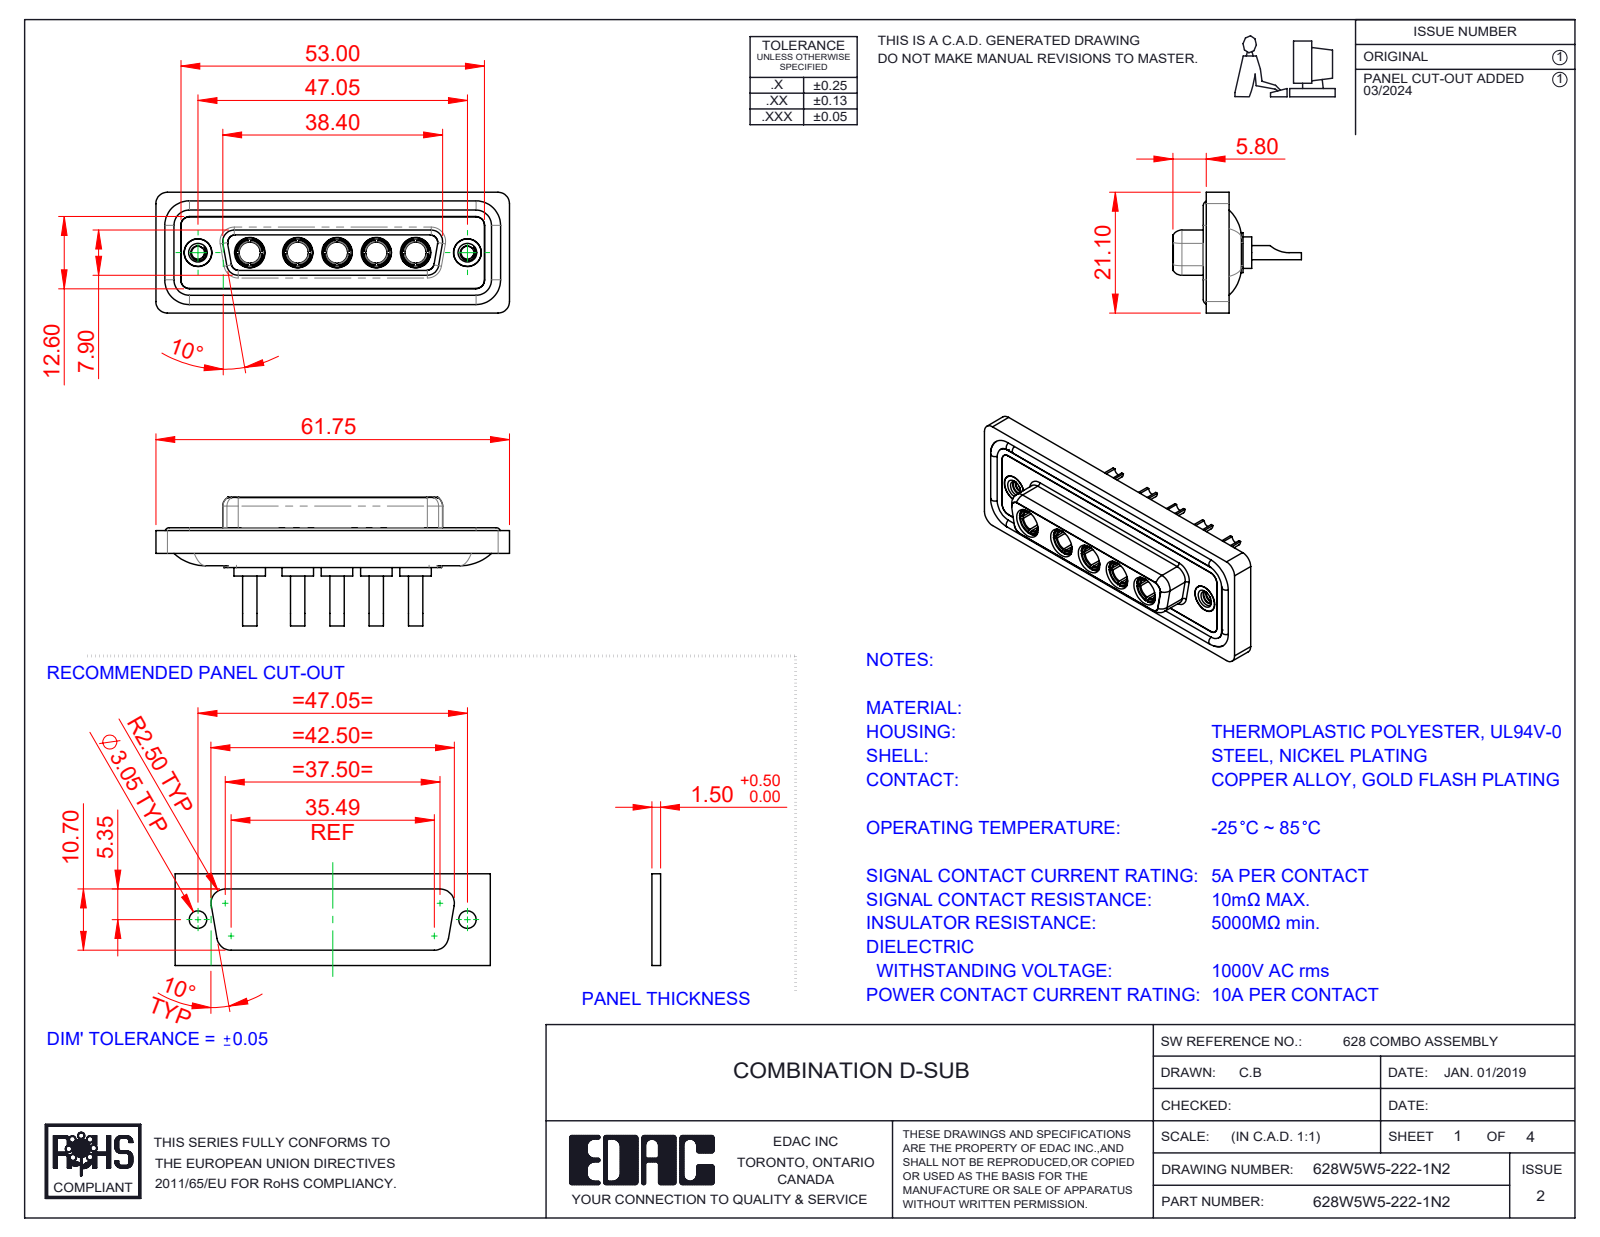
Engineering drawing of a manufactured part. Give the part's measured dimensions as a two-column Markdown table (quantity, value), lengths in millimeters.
| quantity | value |
| --- | --- |
| part name | Power Socket_10A SC; 628W5W5-222-1N2; 628Combo Waterproof Housing_25 Contacts; 628Combo Shell Front_25 Contacts (+3 more) |
| STEP written by | SolidWorks 2023 (CONFIG_CONTROL_DESIGN) |
| units | millimeters |
| bodies | 17 solids, 781 faces (260 planar, 318 cylindrical, 203 other) |
| overall size | 61.75 × 22.45 × 21.1 |
| volume | 8 159 mm³ |
| surface area | 13 654 mm² |
| round holes (diameter × count) | 4.85 × 7, 1.7 × 5, 3.7 × 5, 5.3 × 5, 2.26 × 2, 4 × 2, 4.05 × 2, 5 × 2 |
| round bosses / shafts (diameter × count) | 5.5 × 5, 5.2 × 5, 4.96 × 5, 4.75 × 5, 3.75 × 5, 2.5 × 5, 1.6 × 4, 4.95 × 2 |
| partial cylindrical surfaces (radius × count) | 1.5 × 22, 2 × 18, 1.35 × 8, 1.6 × 8, 2.1 × 5, 0.25 × 4, 0.5 × 4, 0.6 × 4 |
| main face-to-face distances | 0.4, 1.8, 7.45, 5.65, 0.5, 7.05, 6.6, 1.6, 1.1, 2.9 |
| hole center spacings | 6.86, 9.04, 13.72, 38.01, 8.39, 15.25, 15.9, 17.43 |
